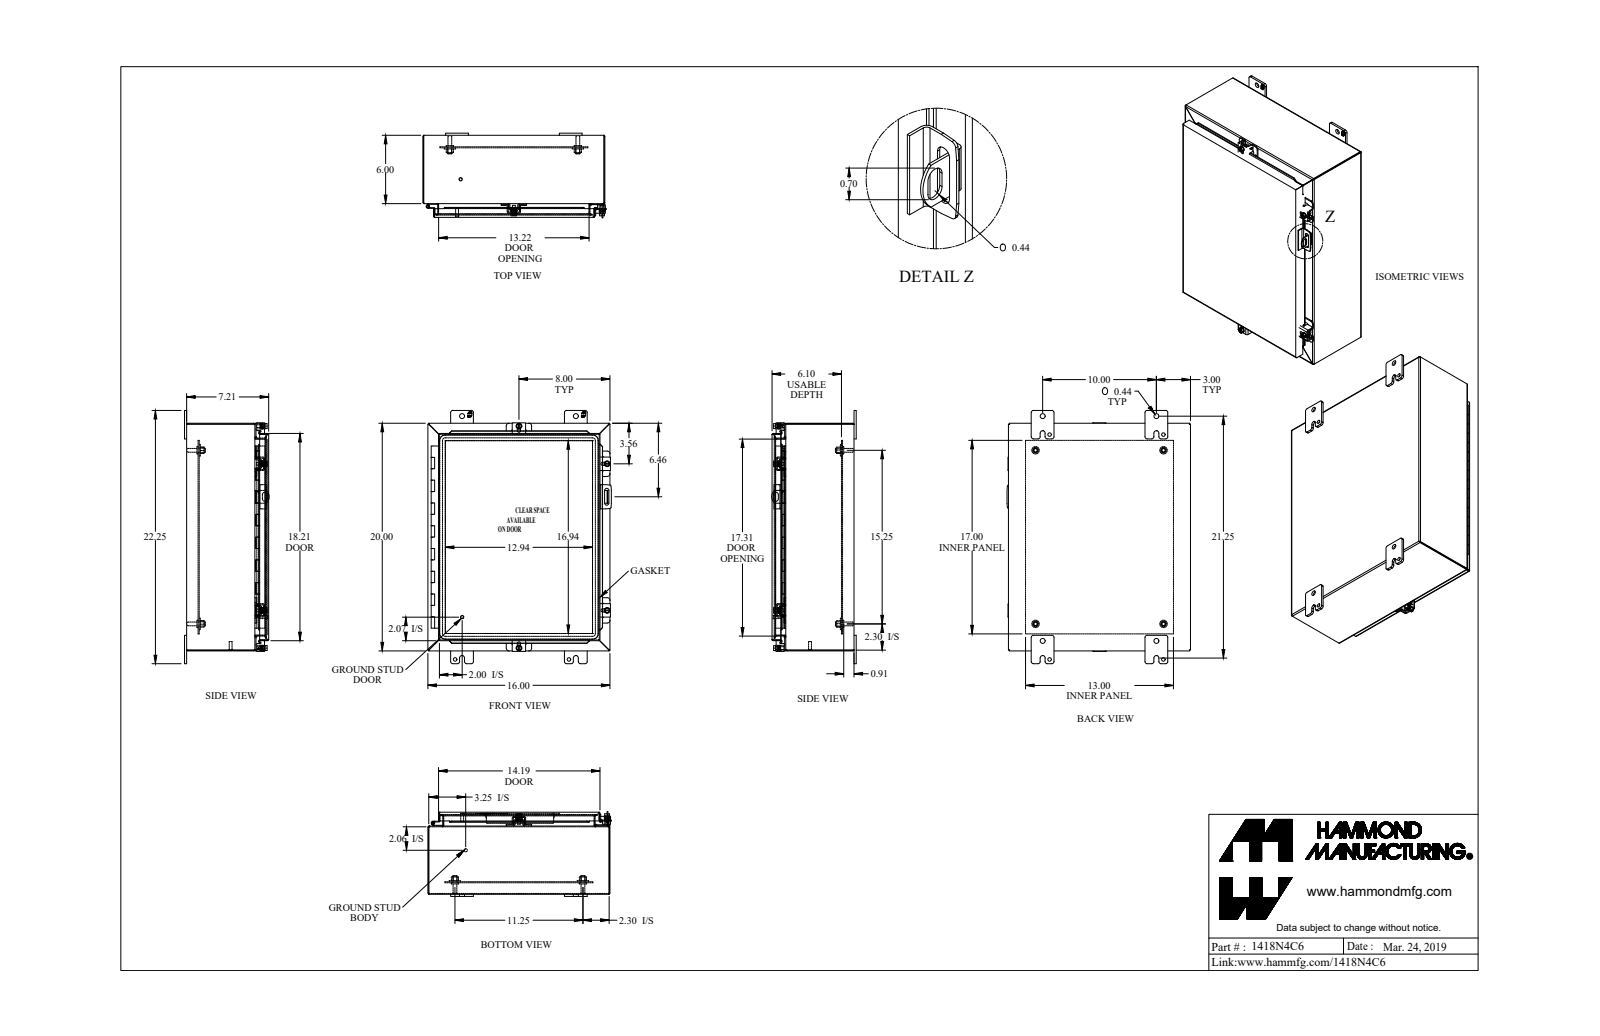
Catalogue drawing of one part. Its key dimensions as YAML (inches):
part_name: "1418N4C6_Default"
step_written_by: "SolidWorks 2019 (CONFIG_CONTROL_DESIGN)"
units: inches
bodies: {solids: 39, faces: 1368, planar: 833, cylindrical: 451, other: 84}
overall_size: [22.25, 16.126, 7.437]
volume: 123.1
surface_area: 3229
round_holes:
  - {diameter: 0.213, count: 4}
  - {diameter: 0.265, count: 4}
  - {diameter: 0.313, count: 4}
  - {diameter: 0.375, count: 4}
  - {diameter: 0.437, count: 4}
  - {diameter: 0.5, count: 4}
  - {diameter: 0.307, count: 2}
  - {diameter: 0.445, count: 2}
  - {diameter: 0.125, count: 1}
  - {diameter: 0.187, count: 1}
round_bosses_or_shafts:
  - {diameter: 0.65, count: 4}
  - {diameter: 0.5, count: 4}
  - {diameter: 0.39, count: 4}
  - {diameter: 0.375, count: 4}
  - {diameter: 0.33, count: 4}
  - {diameter: 0.244, count: 4}
  - {diameter: 1, count: 2}
  - {diameter: 0.281, count: 2}
partial_cylinders:
  - {radius: 0.188, count: 26}
  - {radius: 0.036, count: 24}
  - {radius: 0.108, count: 24}
  - {radius: 0.048, count: 21}
  - {radius: 0.143, count: 21}
  - {radius: 0.25, count: 20}
  - {radius: 0.045, count: 8}
  - {radius: 0.125, count: 8}
face_to_face_distances: [0.072, 0.072, 7.066, 7.138, 7.138, 7.21, 15.928, 0.095, 6.106, 6.034]
hole_center_spacings: [18.951, 1.736, 10, 15.25, 18.263, 19.75, 22.137, 2.434]
